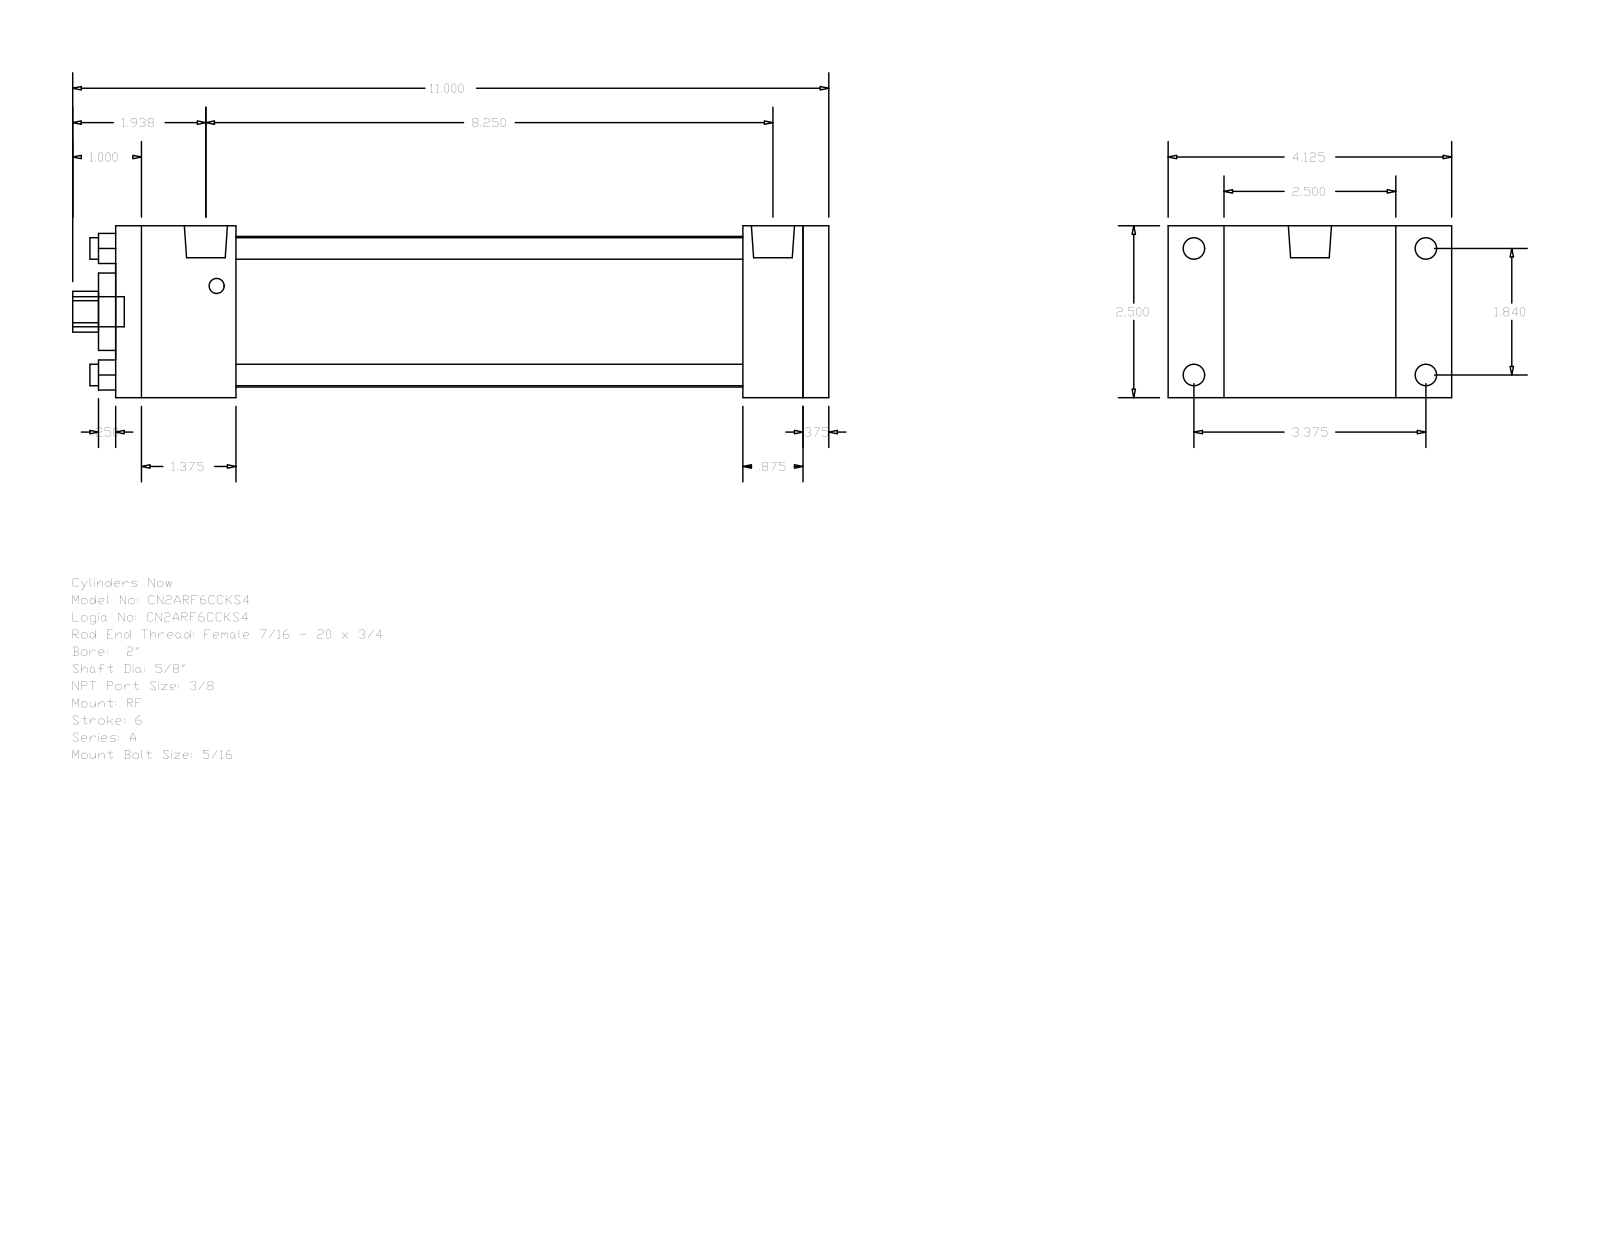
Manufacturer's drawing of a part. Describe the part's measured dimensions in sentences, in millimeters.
The part is named "A_RF__0200_0.625". Its 3-D file was written by "GSSL Pune (CONFIG_CONTROL_DESIGN)". It is 0 solids with 92 faces: 64 planar, 28 cylindrical and 0 other. Overall it measures 279.4 by 104.78 by 63.5 millimeters. Round holes: 4 of diameter 7.94, 1 of diameter 15.88, 1 of diameter 28.57, 1 of diameter 55.63. Round bosses or shafts: 4 of diameter 7.94, 4 of diameter 5.56, 2 of diameter 15.93, 1 of diameter 11.11. Partial cylindrical surfaces (rounded edges, fillets, slot ends): 1 of radius 7.54. The main face-to-face distances are 63.5, 263.52, 9.52, 254, 44.45, 209.55, 219.07, 231.77, 187.32, 22.23. The hole center spacings are 33.05, 46.74, 66.1.
